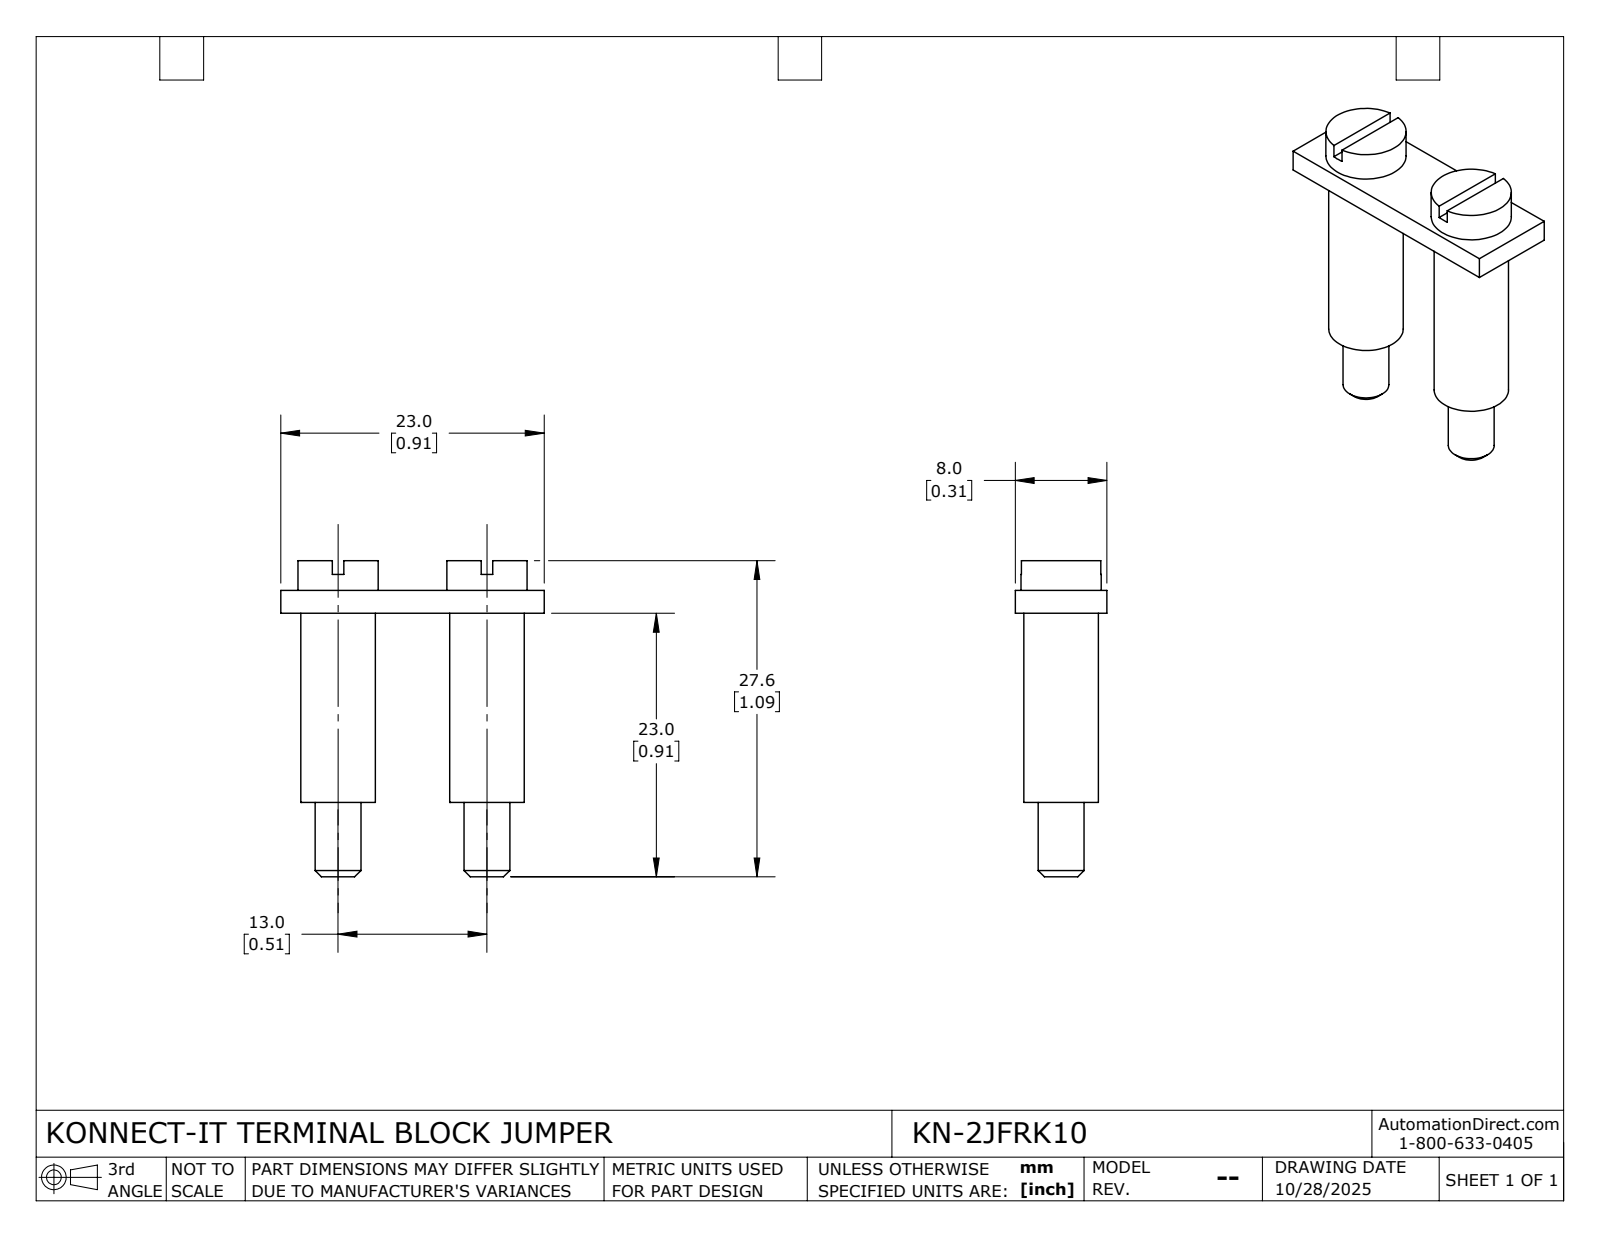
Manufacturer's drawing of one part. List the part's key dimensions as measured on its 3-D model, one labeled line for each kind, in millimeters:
Part name (STEP PRODUCT): KN-2JFRK10
STEP written by: SolidWorks 2024 (CONFIG_CONTROL_DESIGN)
Units: millimetres
Bodies: 1 solid, 36 faces (20 planar, 12 cylindrical, 4 other)
Overall size (bounding box): 27.6 × 23 × 8
Volume: 1 806 mm³ · Surface area: 1 463 mm²
Round bosses / shafts (diameter × count): ⌀7 ×2, ⌀6.5 ×2, ⌀4 ×2
Main face-to-face distances: 2, 4.6, 2.6, 18.5, 8, 16.5, 21.1, 23, 4.5, 5.5
